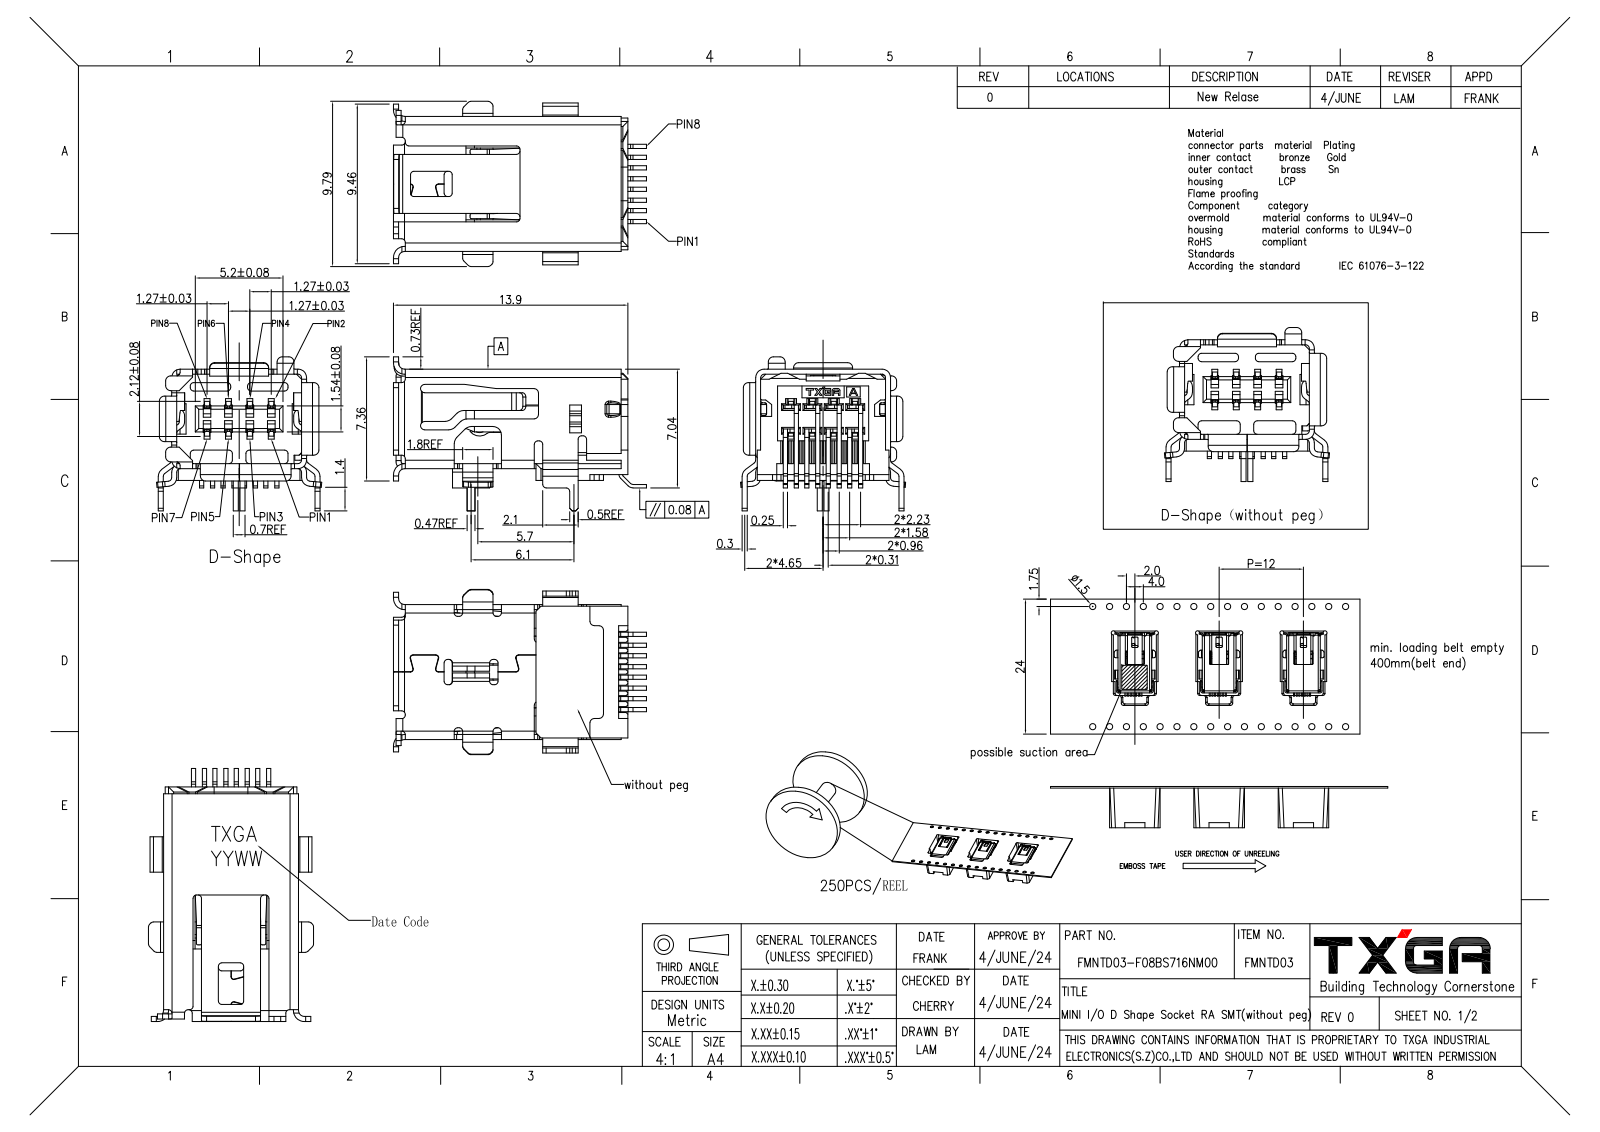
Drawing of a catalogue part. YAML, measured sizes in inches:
part_name: "FMINI-SDRA0XXX-000"
step_written_by: "PRO/ENGINEER BY PARAMETRIC TECHNOLOGY CORPORATION, 2010280 (CONFIG_CONTROL_DESIGN)"
units: inches
bodies: {solids: 1, faces: 1575, planar: 1161, cylindrical: 390, other: 24}
overall_size: [0.591, 0.385, 0.359]
volume: 0.011
surface_area: 1.919
partial_cylinders:
  - {radius: 0.008, count: 91}
  - {radius: 0.004, count: 68}
  - {radius: 0.02, count: 30}
  - {radius: 0.006, count: 24}
  - {radius: 0.012, count: 18}
  - {radius: 0.01, count: 12}
  - {radius: 0.016, count: 10}
  - {radius: 0.007, count: 8}
face_to_face_distances: [0.22, 0.209, 0.303, 0.232, 0.039, 0.26, 0.248, 0.315, 0.028, 0.291]
